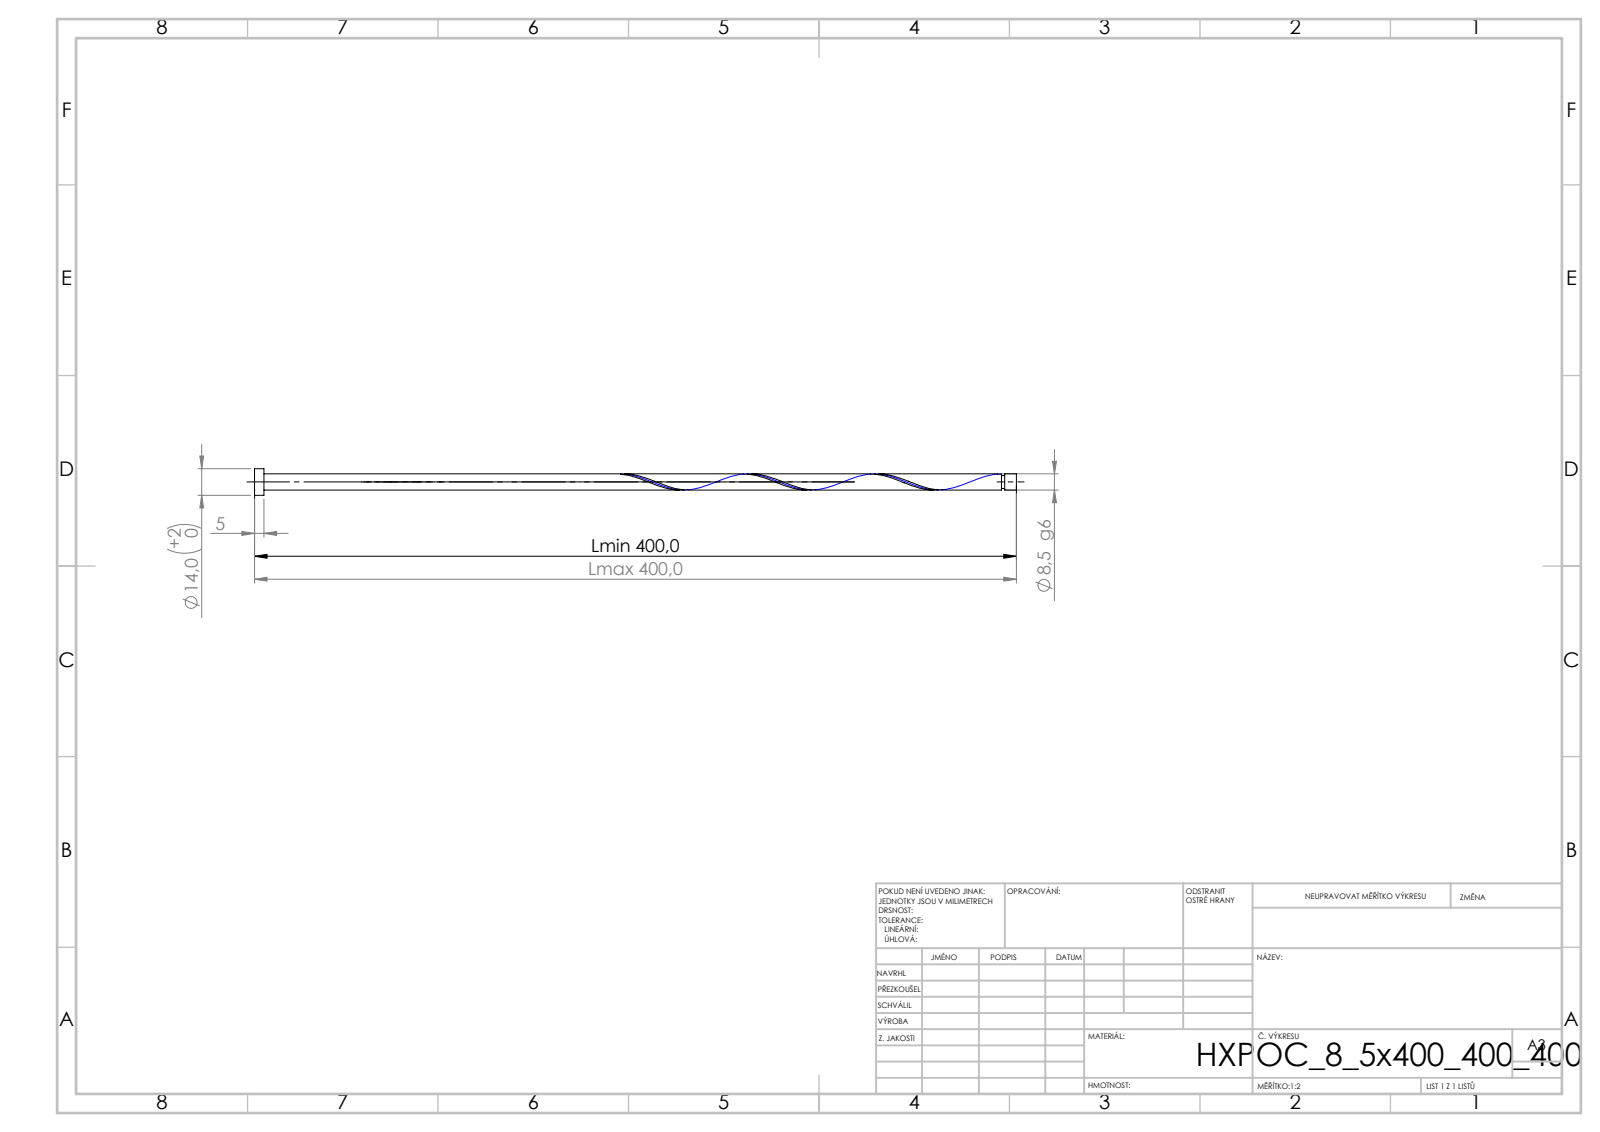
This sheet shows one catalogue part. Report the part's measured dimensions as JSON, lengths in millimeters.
{"step_written_by": "SolidWorks 2019 (CONFIG_CONTROL_DESIGN)", "units": "millimeters", "bodies": {"solids": 1, "faces": 21, "planar": 6, "cylindrical": 14, "other": 1}, "overall_size": [400, 14, 14], "volume_mm3": 22932, "surface_area_mm2": 11285, "round_bosses_or_shafts": [[14, 1], [8.5, 1], [6.8, 1]], "face_to_face_distances": [5, 400, 395, 393.86, 388.86, 6.14, 392.16, 387.16, 1.7, 7.84]}
